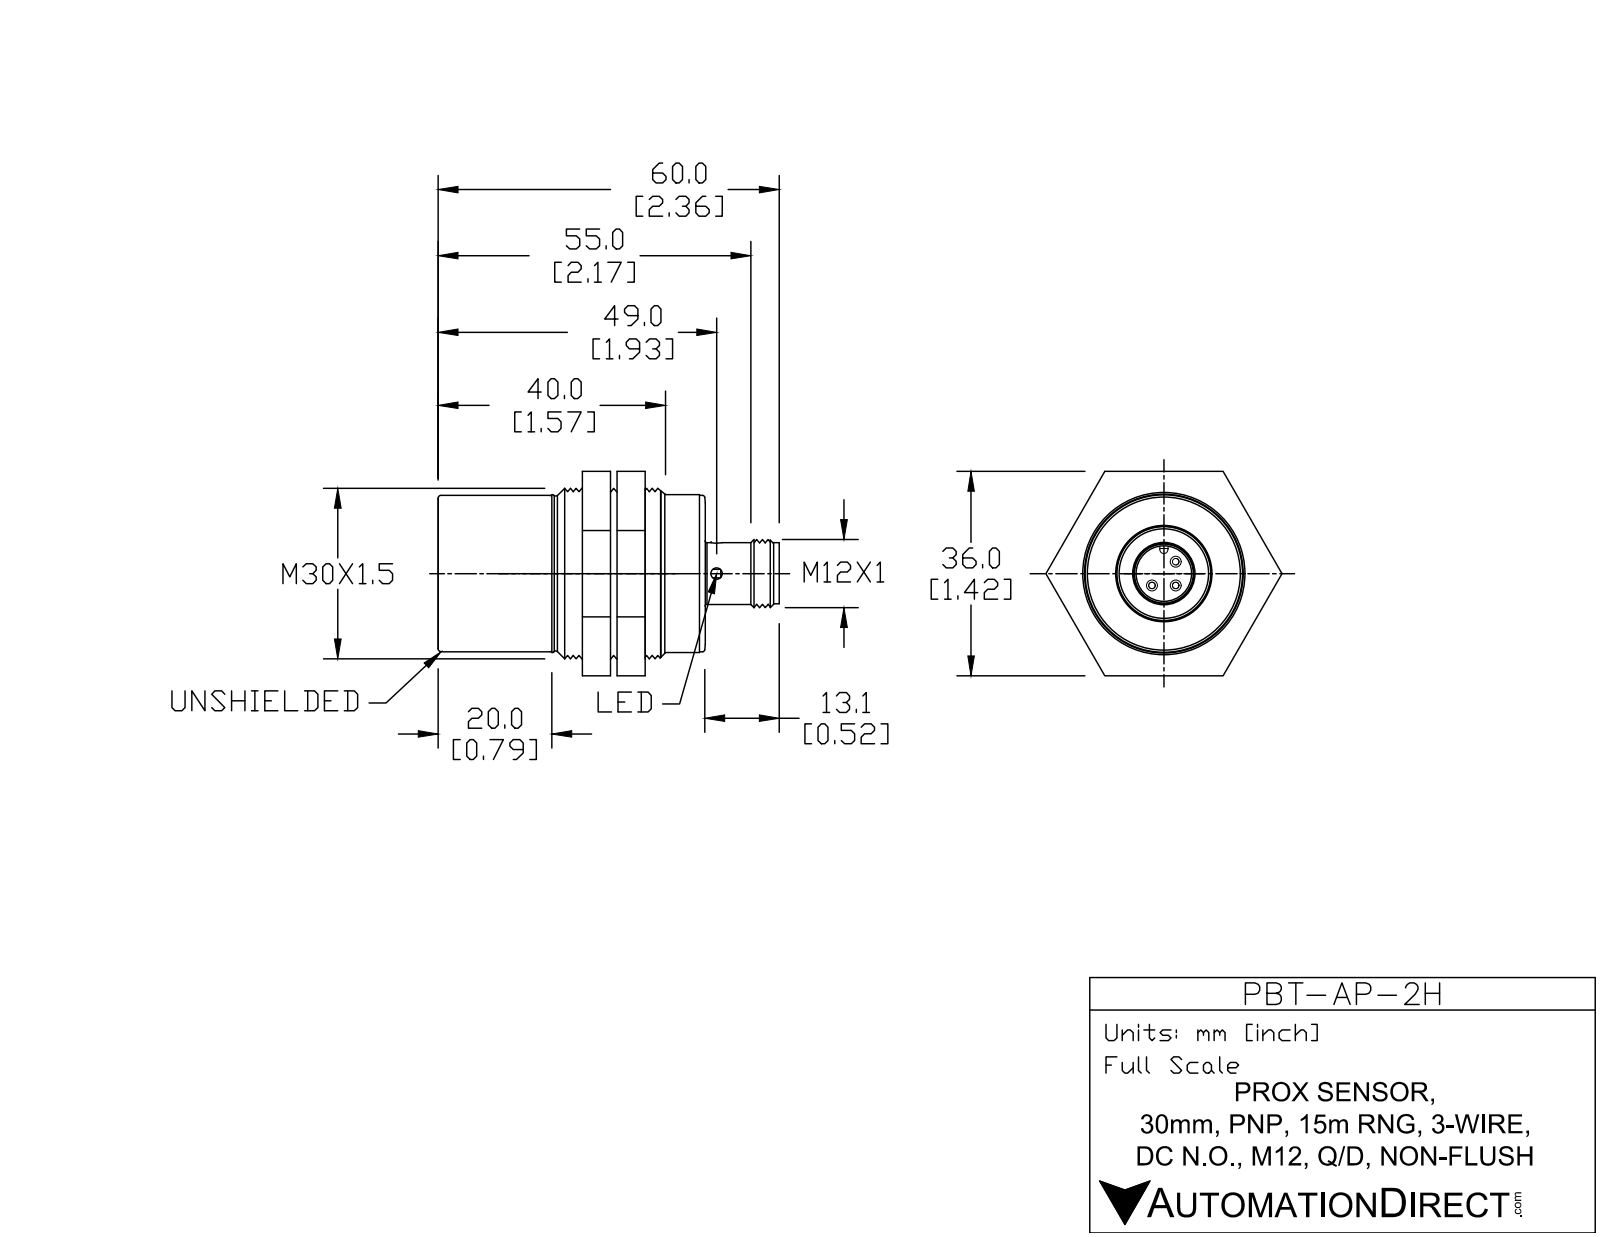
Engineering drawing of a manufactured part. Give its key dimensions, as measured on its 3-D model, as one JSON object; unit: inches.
{"part_name": "PBT-AP-2H", "step_written_by": "SolidWorks 2011 (AUTOMOTIVE_DESIGN)", "units": "inches", "bodies": {"solids": 8, "faces": 67, "planar": 39, "cylindrical": 18, "other": 10}, "overall_size": [2.343, 1.636, 1.443], "volume_in3": 2.139, "surface_area_in2": 18.35, "round_holes": [[0.049, 1], [0.335, 1], [0.423, 1], [1.122, 1]], "round_bosses_or_shafts": [[0.039, 3], [1.181, 1], [1.102, 1], [1.083, 1], [1.081, 1], [0.472, 1], [0.429, 1], [0.415, 1]], "partial_cylinders_radius": [[0.02, 1]], "face_to_face_distances": [0.394, 0.787, 1.063, 0.177, 0.571, 1.85, 0.492, 1.457, 0.886, 1.28]}
